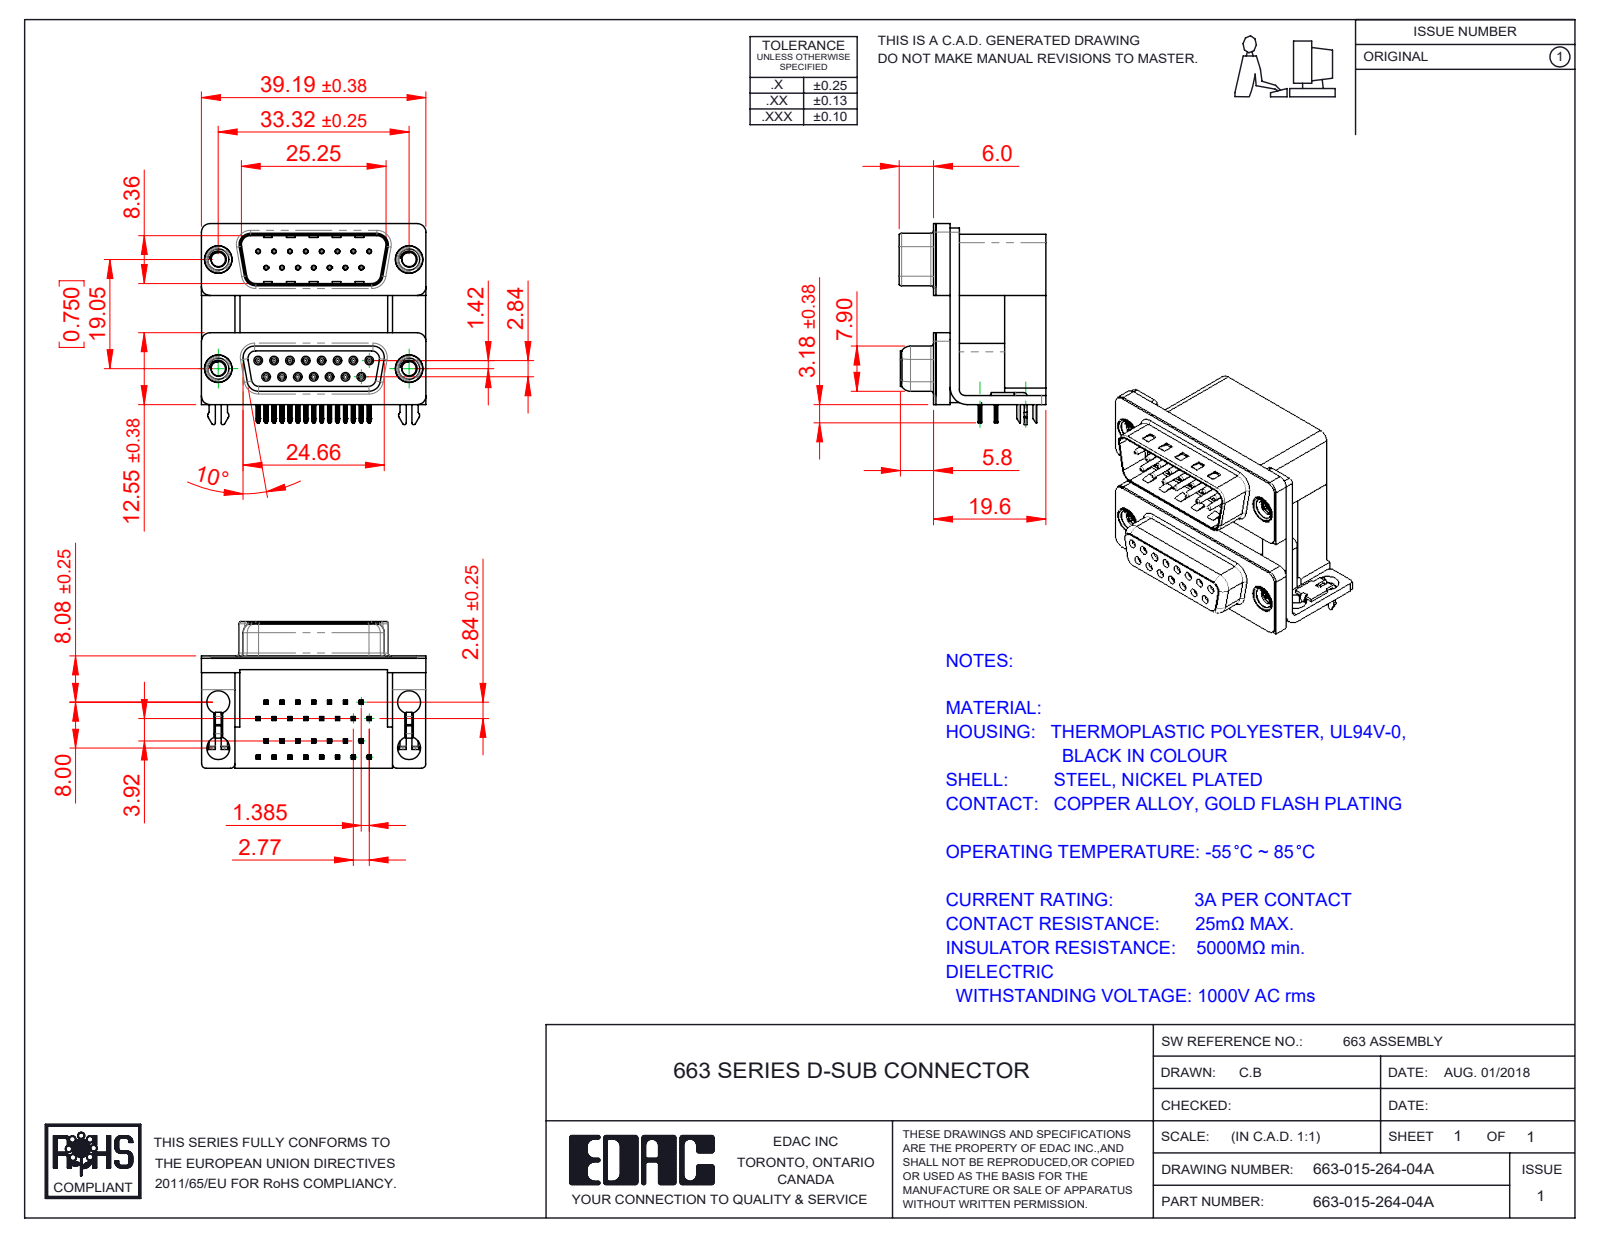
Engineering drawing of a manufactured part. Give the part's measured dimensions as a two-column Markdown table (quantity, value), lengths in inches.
| quantity | value |
| --- | --- |
| part name | 663 Contact Top Upper_M; 663 Shell Plug_15 Contacts; 663 2 Prong Board Lock_4; 663 Housing Upper_15 Contacts M (+8 more) |
| STEP written by | SolidWorks 2020 (CONFIG_CONTROL_DESIGN) |
| units | inches |
| bodies | 43 solids, 4024 faces (2093 planar, 1052 cylindrical, 879 other) |
| overall size | 1.543 × 1.382 × 1.008 |
| volume | 0.928 in³ |
| surface area | 26.21 in² |
| round holes (diameter × count) | 0.031 × 30, 0.014 × 15, 0.035 × 15, 0.157 × 8, 0.098 × 4, 0.138 × 4, 0.189 × 4, 0.197 × 4 |
| round bosses / shafts (diameter × count) | 0.047 × 15, 0.03 × 15, 0.193 × 4, 0.187 × 4, 0.154 × 4 |
| partial cylindrical surfaces (radius × count) | 0.004 × 121, 0.01 × 66, 0.006 × 60, 0.005 × 30, 0.014 × 30, 0.02 × 16, 0.059 × 16, 0.013 × 15 |
| main face-to-face distances | 0.016, 0.756, 0.657, 0.098, 0.283, 0.472, 0.374, 0.421, 0.063, 0.114 |
| hole center spacings | 0.124, 0.758, 0.109, 0.781, 0.218, 0.327, 0.75, 0.818 |
